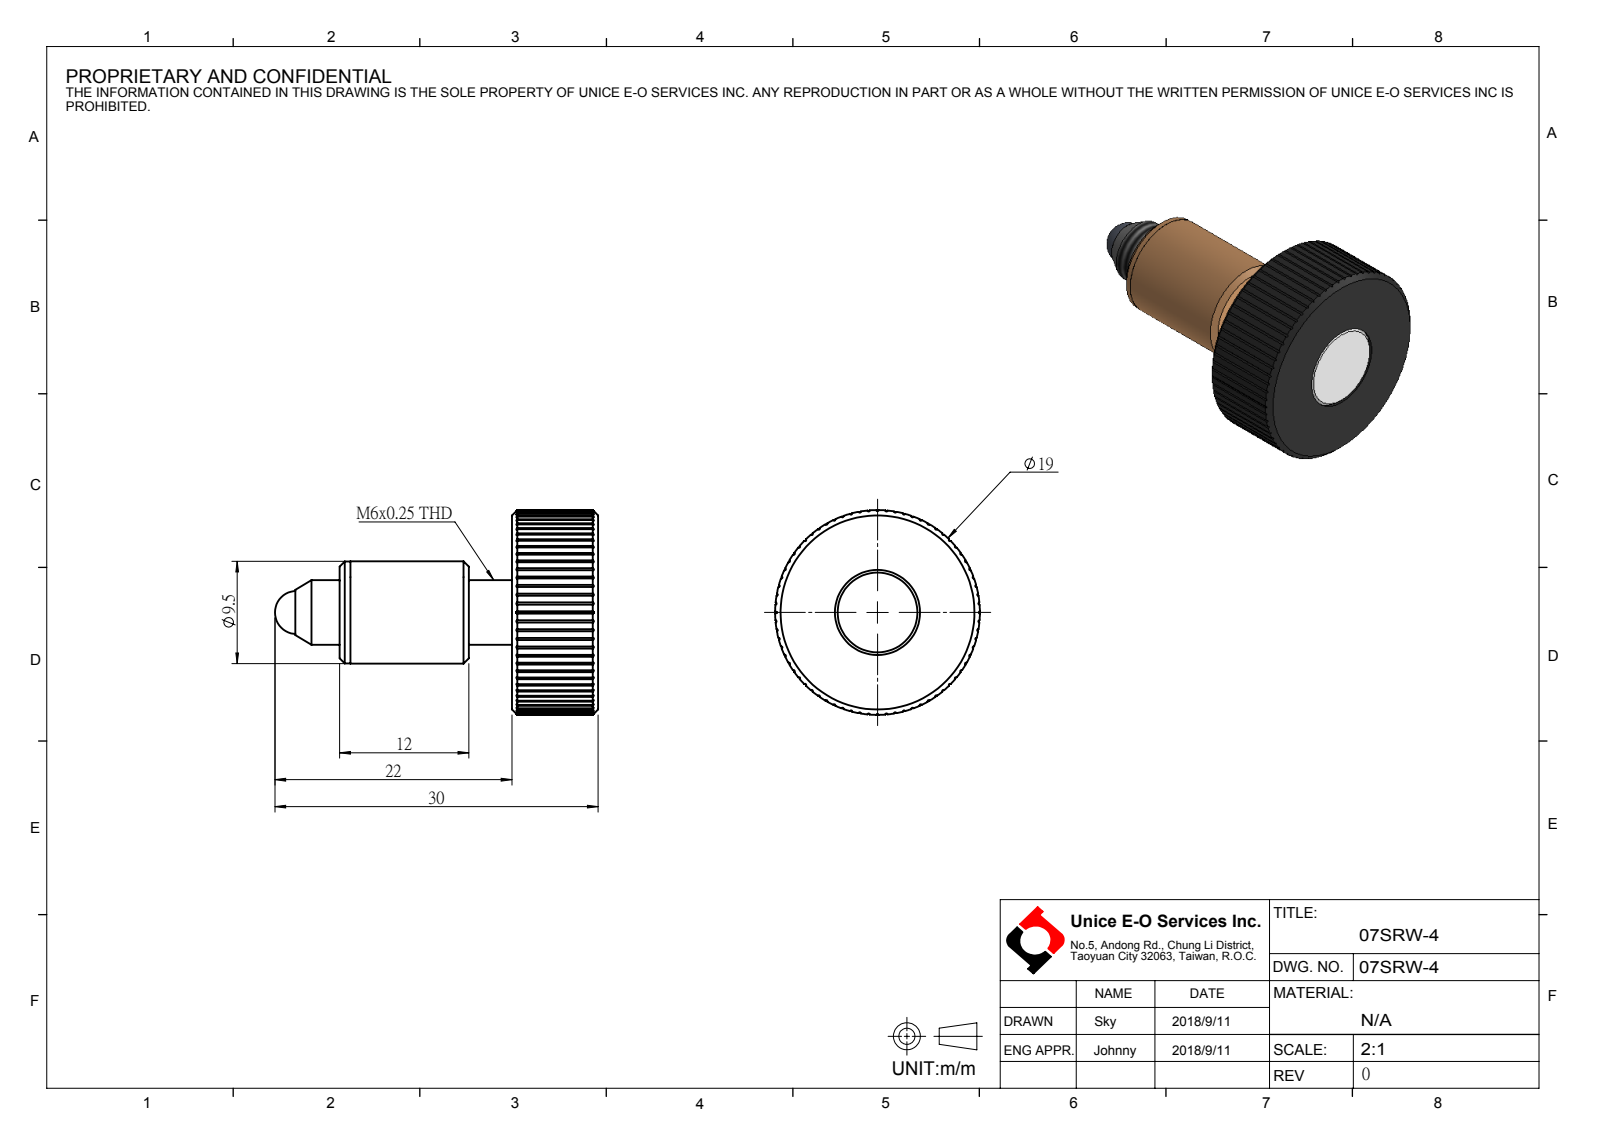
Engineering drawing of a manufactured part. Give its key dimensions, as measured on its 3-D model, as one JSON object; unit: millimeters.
{"part_name": "07SRW-4", "step_written_by": "SolidWorks 2016 (AUTOMOTIVE_DESIGN)", "units": "millimeters", "bodies": {"solids": 0, "faces": 215, "planar": 9, "cylindrical": 190, "other": 16}, "overall_size": [30, 19, 19], "round_holes": [[6.35, 1], [7.9, 1]], "round_bosses_or_shafts": [[9.5, 1], [9.45, 1], [6, 1]], "partial_cylinders_radius": [[0.1, 72], [9.5, 1]], "face_to_face_distances": [8, 12, 16, 24, 4, 4.1, 16.1, 20.1, 28.1, 5.1]}
